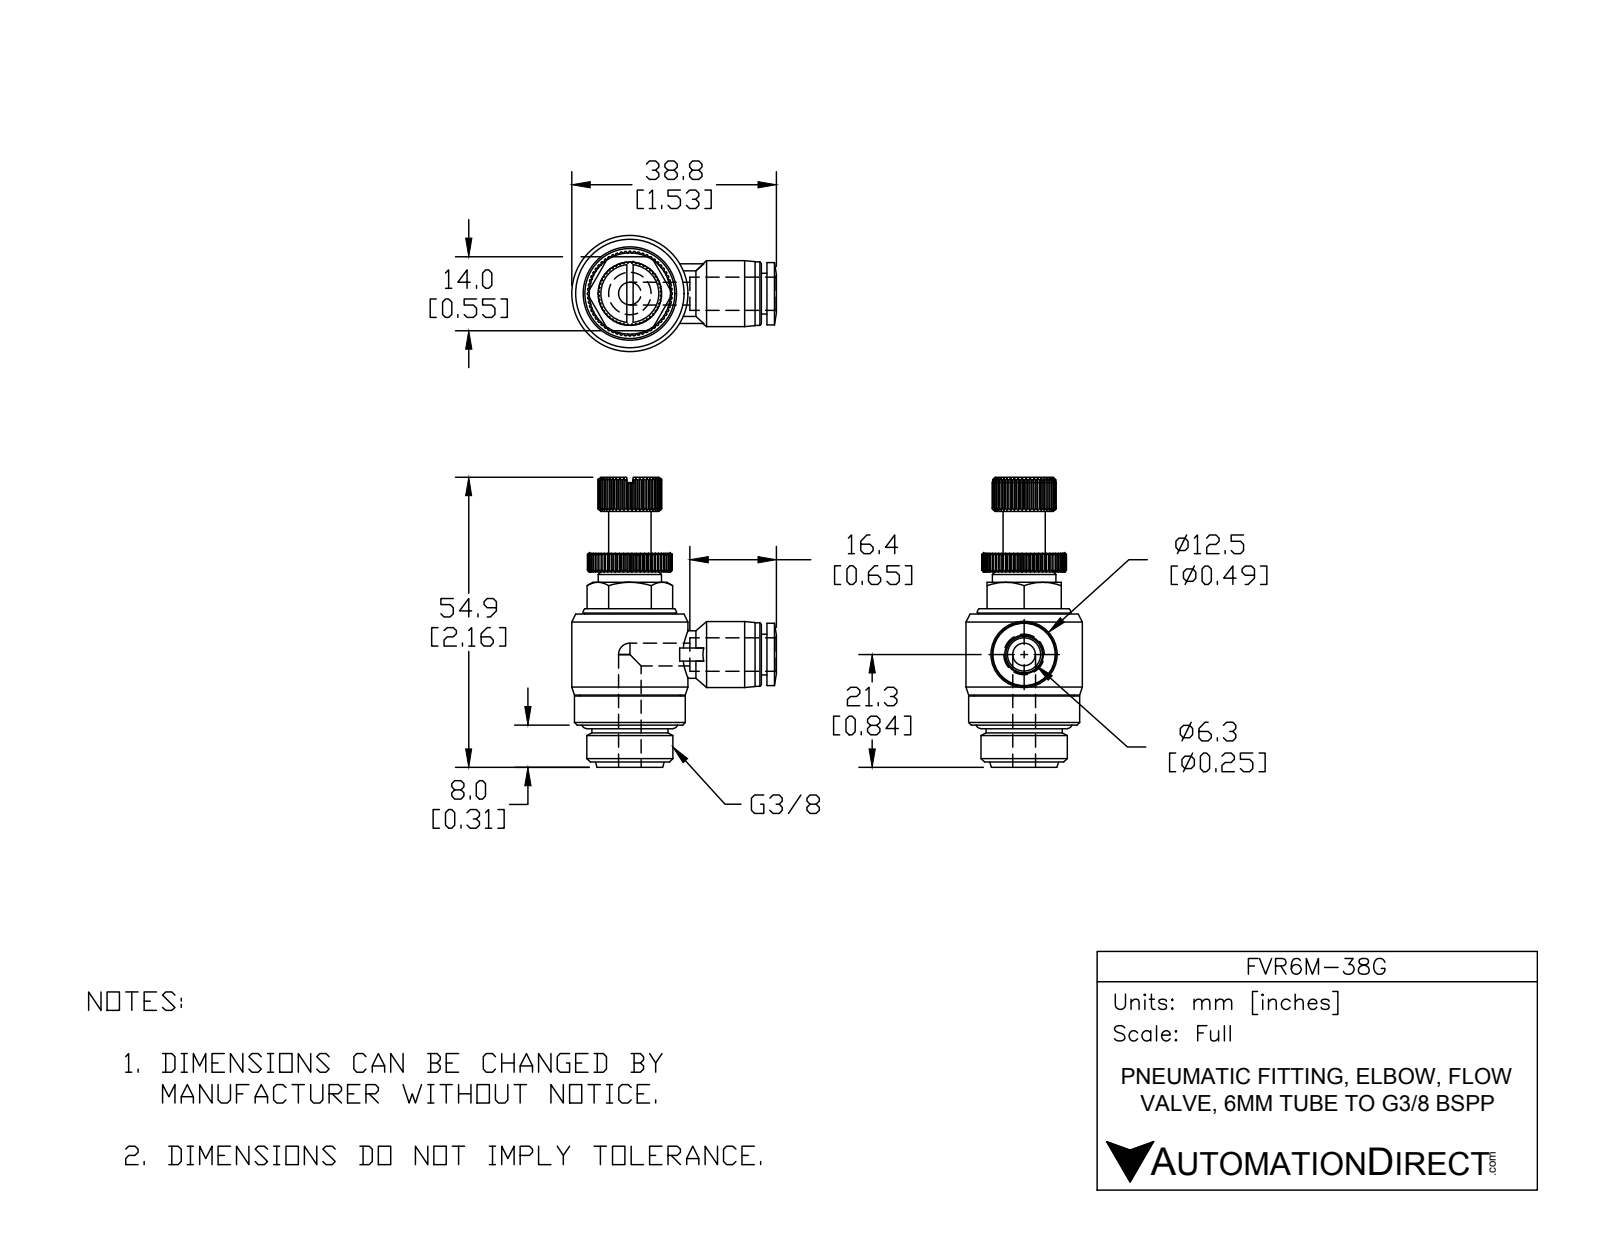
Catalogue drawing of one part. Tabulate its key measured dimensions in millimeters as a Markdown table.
| quantity | value |
| --- | --- |
| part name | FVR6M-38G |
| STEP written by | SolidWorks 2015 (AUTOMOTIVE_DESIGN) |
| units | millimeters |
| bodies | 2 solids, 567 faces (251 planar, 143 cylindrical, 173 other) |
| overall size | 54.9 × 38.8 × 22 |
| volume | 13 100 mm³ |
| surface area | 5 970 mm² |
| round holes (diameter × count) | 4.3 × 2, 6.3 × 1 |
| round bosses / shafts (diameter × count) | 12 × 2, 22 × 1, 21 × 1, 19 × 1, 17.1 × 1, 16.3 × 1, 14.4 × 1, 12.5 × 1 |
| partial cylindrical surfaces (radius × count) | 8 × 1 |
| main face-to-face distances | 29, 8, 14, 1, 40.5, 27, 11.5, 7, 5.5, 37 |
